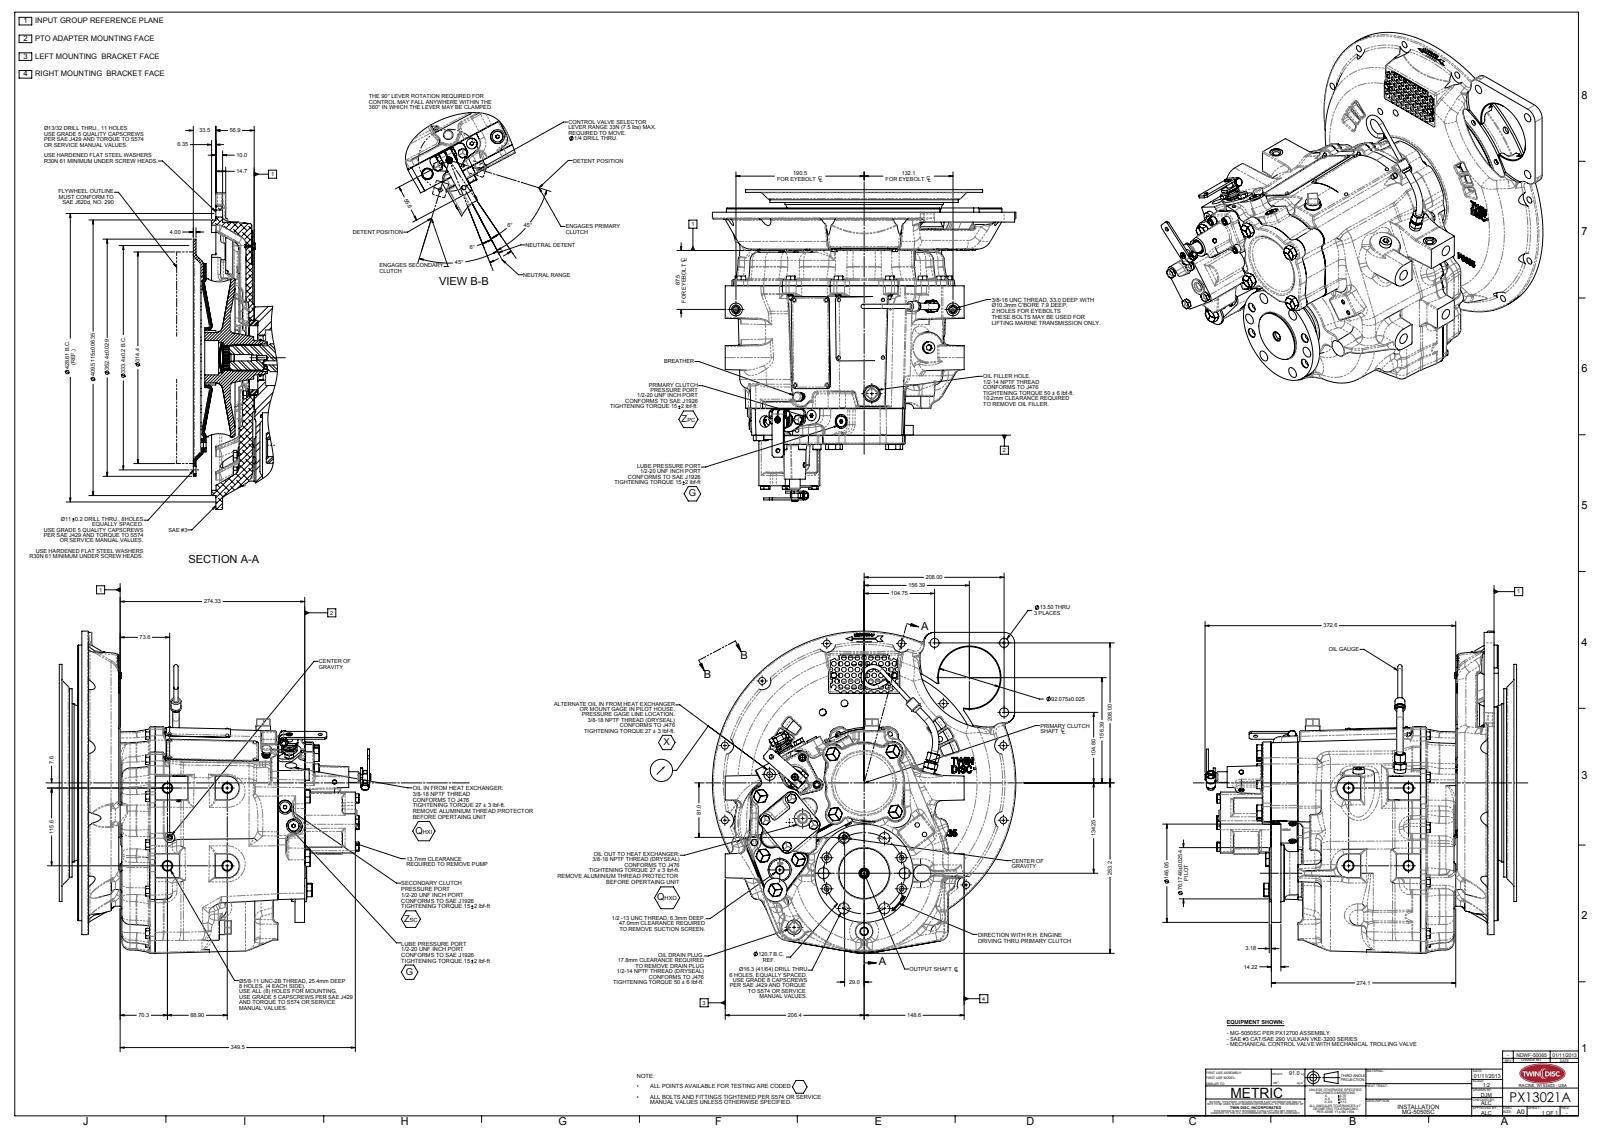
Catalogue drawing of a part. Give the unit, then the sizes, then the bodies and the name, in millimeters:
Units: millimetres
Overall size (bounding box): 478.74 × 463.03 × 451
Round holes (diameter × count): ⌀7 ×51, ⌀10.32 ×14, ⌀8.2 ×12, ⌀11 ×8, ⌀7.94 ×7, ⌀16.27 ×6, ⌀7.14 ×4, ⌀14.29 ×4, ⌀3.17 ×3, ⌀10.3 ×3, ⌀13.5 ×3, ⌀20.64 ×3
Round bosses / shafts (diameter × count): ⌀18.87 ×7, ⌀12.56 ×5, ⌀6.35 ×4, ⌀15.88 ×3, ⌀11.91 ×3, ⌀16 ×2, ⌀14.14 ×2, ⌀10.99 ×2
Partial cylindrical surfaces — rounded edges, fillets, slot ends (radius × count): R1.5 ×89, R1.52 ×67, R8.13 ×63, R8 ×28, R2.5 ×24, R6.35 ×23, R10.16 ×22, R0.51 ×20
Main face-to-face distances: 4, 236.3, 0.66, 236.96, 4.54, 232.42, 231.76, 15, 11, 182.47
Hole centre spacings: 10, 20, 20.07, 26.51, 30, 10.03, 34.68, 17.34
Bodies: 0 solids, 3991 faces (910 planar, 1124 cylindrical, 1957 other)
Part name (STEP PRODUCT): PX13021A
STEP written by: SolidWorks 2010 (AUTOMOTIVE_DESIGN)
